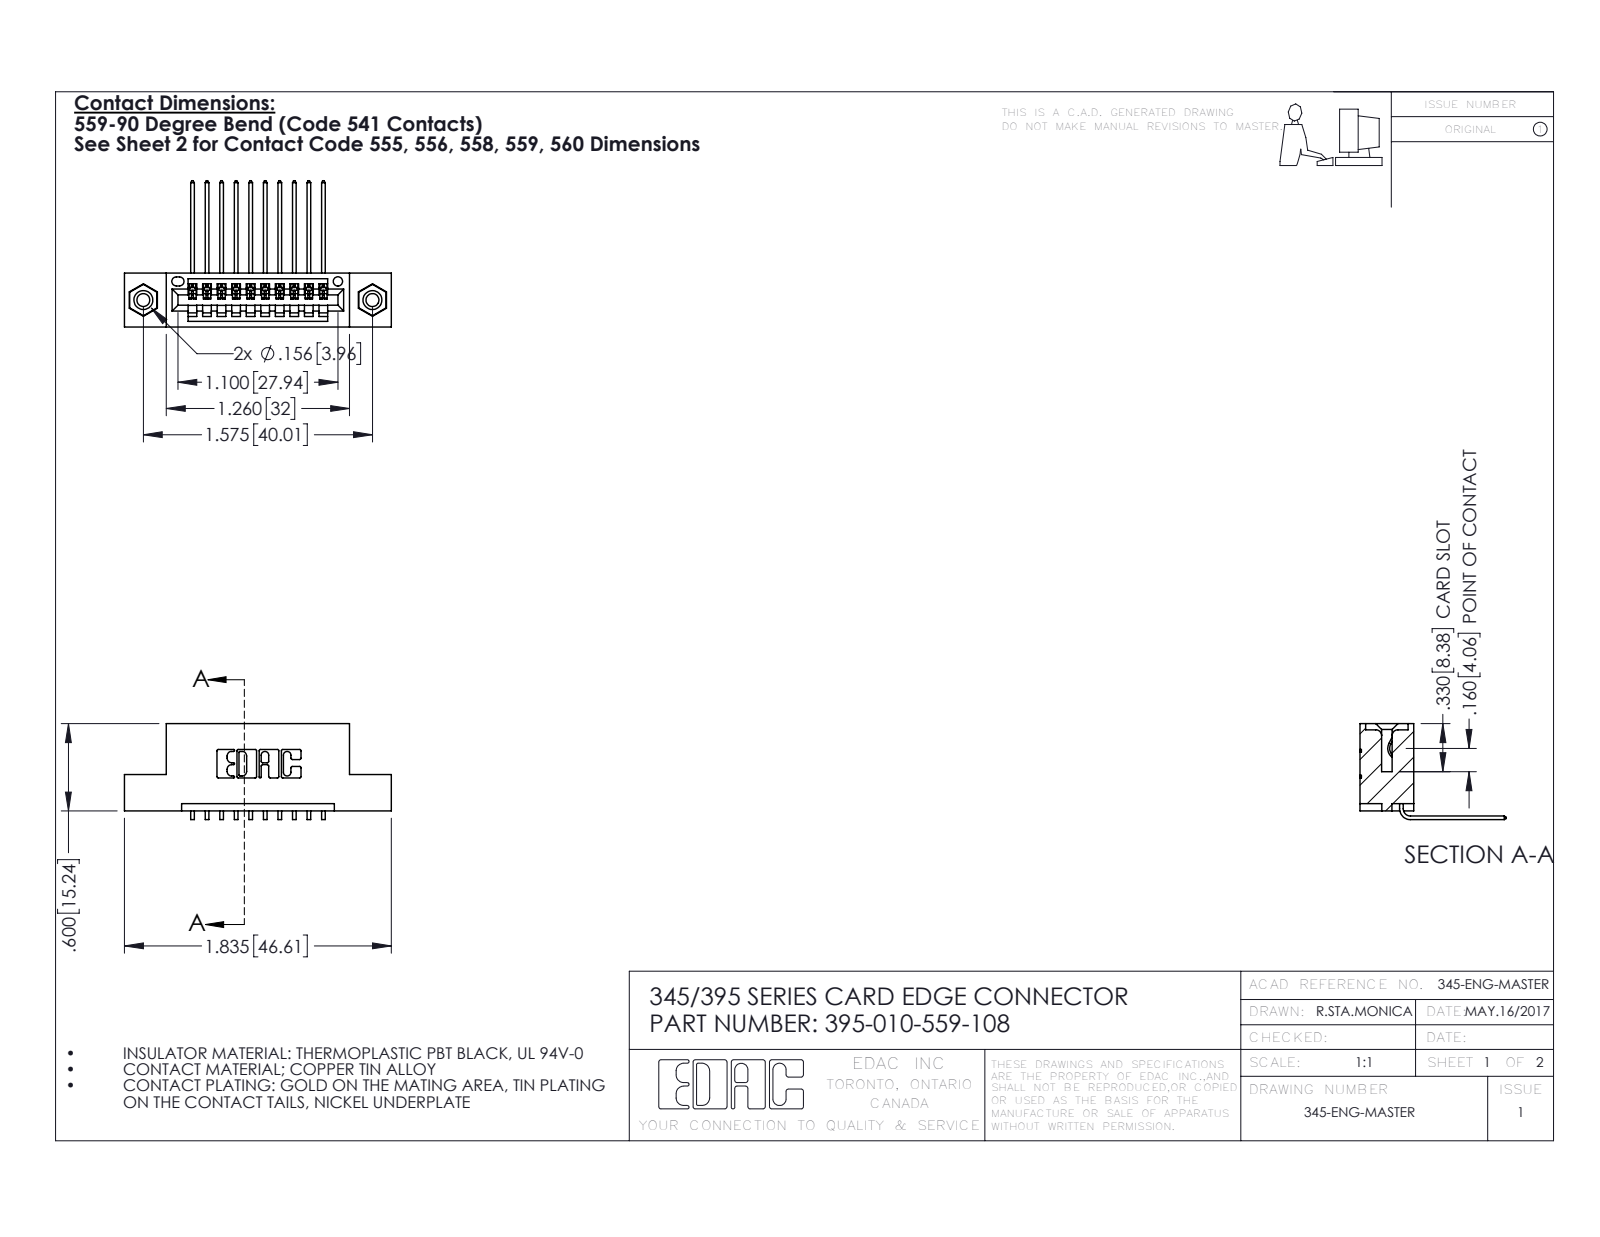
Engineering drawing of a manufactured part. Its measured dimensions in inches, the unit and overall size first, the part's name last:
Units: inches
Overall size (bounding box): 1.835 × 1.005 × 0.659
Round holes (diameter × count): ⌀0.089 ×2, ⌀0.125 ×2, ⌀0.156 ×2, ⌀0.064 ×1
Round bosses / shafts (diameter × count): ⌀0.155 ×2
Partial cylindrical surfaces — rounded edges, fillets, slot ends (radius × count): R0.01 ×22, R0.006 ×20, R0.007 ×6, R0.031 ×6, R0.026 ×3, R0.031 ×2, R0.04 ×2, R0.014 ×1
Main face-to-face distances: 0.2, 0.37, 0.072, 0.298, 0.1, 0.6, 0.098, 0.272, 0.025, 0.06
Hole centre spacings: 0.27, 1.344, 1.575
Volume: 0.256 in³ · Surface area: 8.293 in²
Bodies: 13 solids, 786 faces (532 planar, 238 cylindrical, 16 other)
Part name (STEP PRODUCT): 345-292-001_558 559 Tail - 1; 395-010-559-108; 345 Part_Flush Mounting Lugs - 0.156 Dia-TI; 345-250-001_345-250-003-102
STEP written by: SolidWorks 2016 (CONFIG_CONTROL_DESIGN)
